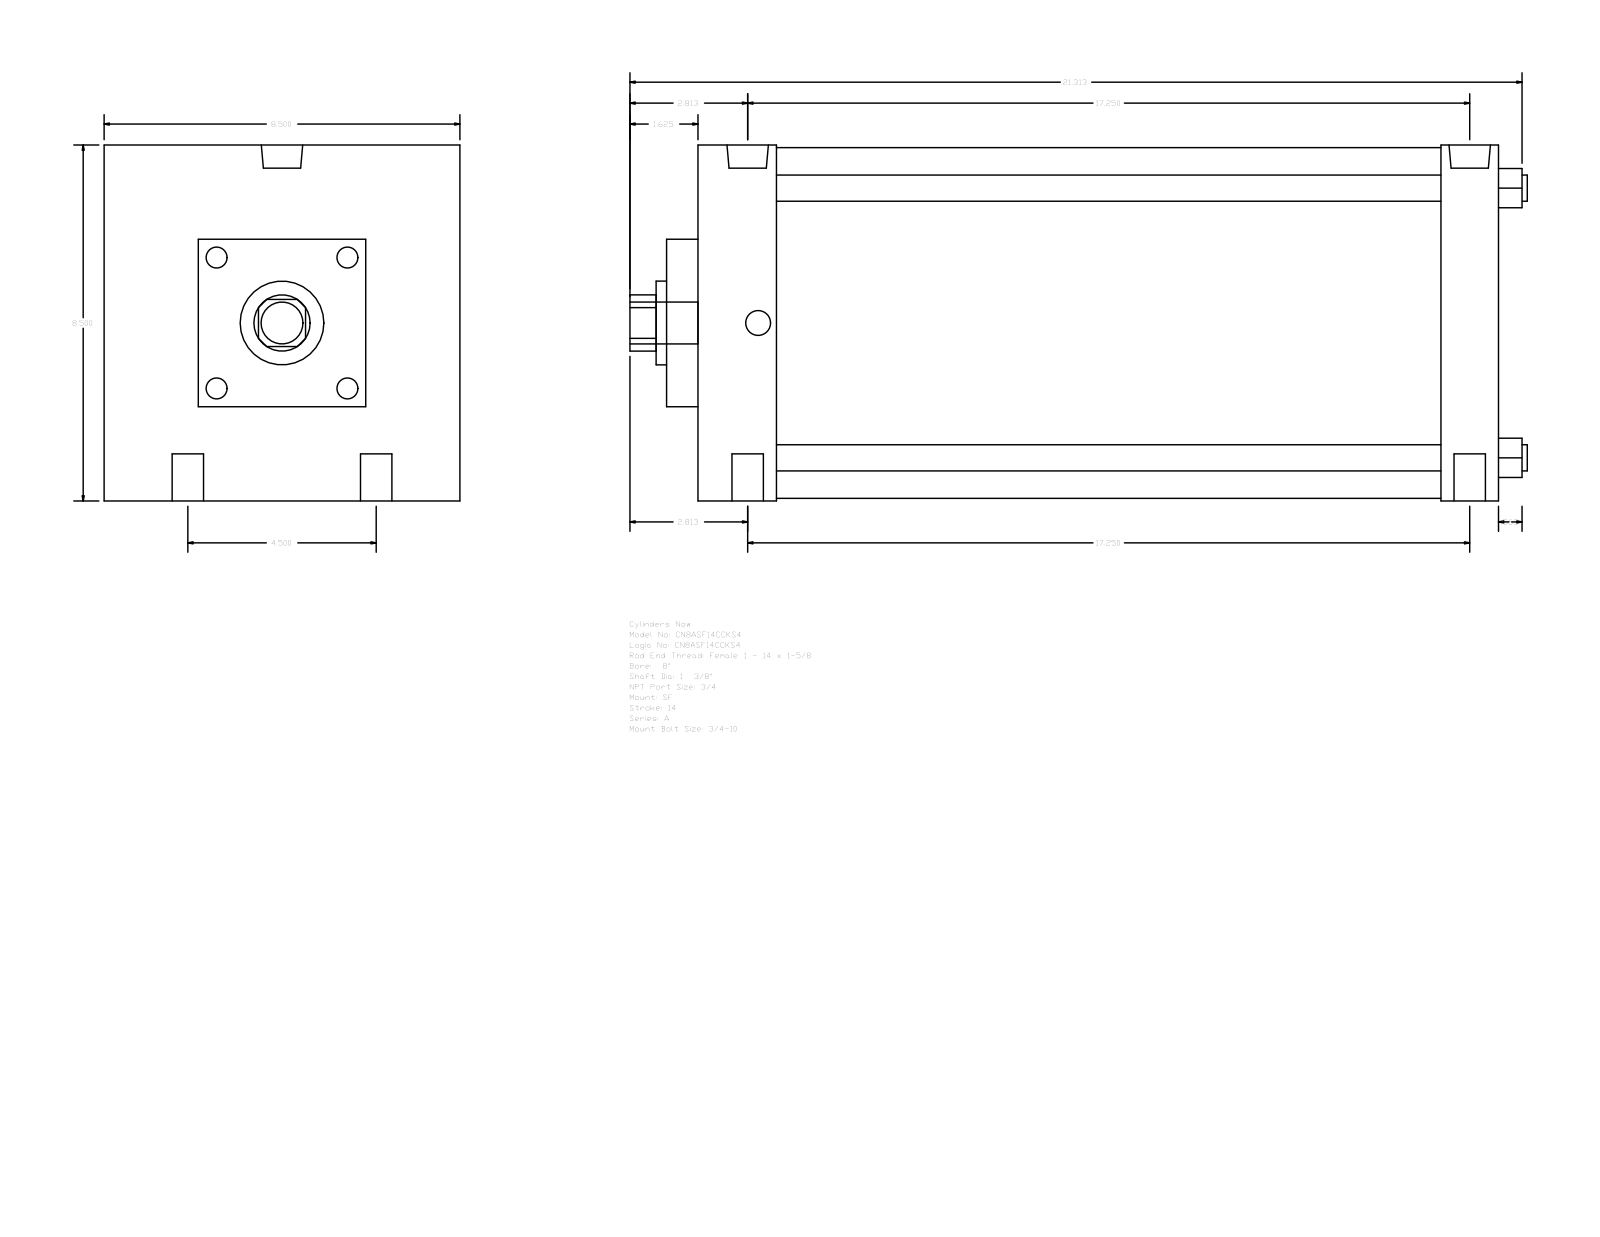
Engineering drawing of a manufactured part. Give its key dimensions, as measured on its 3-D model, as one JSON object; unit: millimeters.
{"part_name": "A_SF__0800_1.375", "step_written_by": "GSSL Pune (CONFIG_CONTROL_DESIGN)", "units": "millimeters", "bodies": {"solids": 0, "faces": 93, "planar": 67, "cylindrical": 26, "other": 0}, "overall_size": [544.51, 215.9, 215.9], "round_holes": [[19.05, 4], [15.08, 2], [25.12, 2], [34.92, 1], [50.8, 1]], "round_bosses_or_shafts": [[15.88, 4], [212.72, 1], [25.4, 1]], "partial_cylinders_radius": [[17.06, 1]], "face_to_face_distances": [485.78, 215.9, 47.63, 450.85, 403.22, 438.15, 34.93, 19.04, 66.67, 469.89], "hole_center_spacings": [57.15, 441.86, 438.15, 114.3, 452.81, 425.45]}
